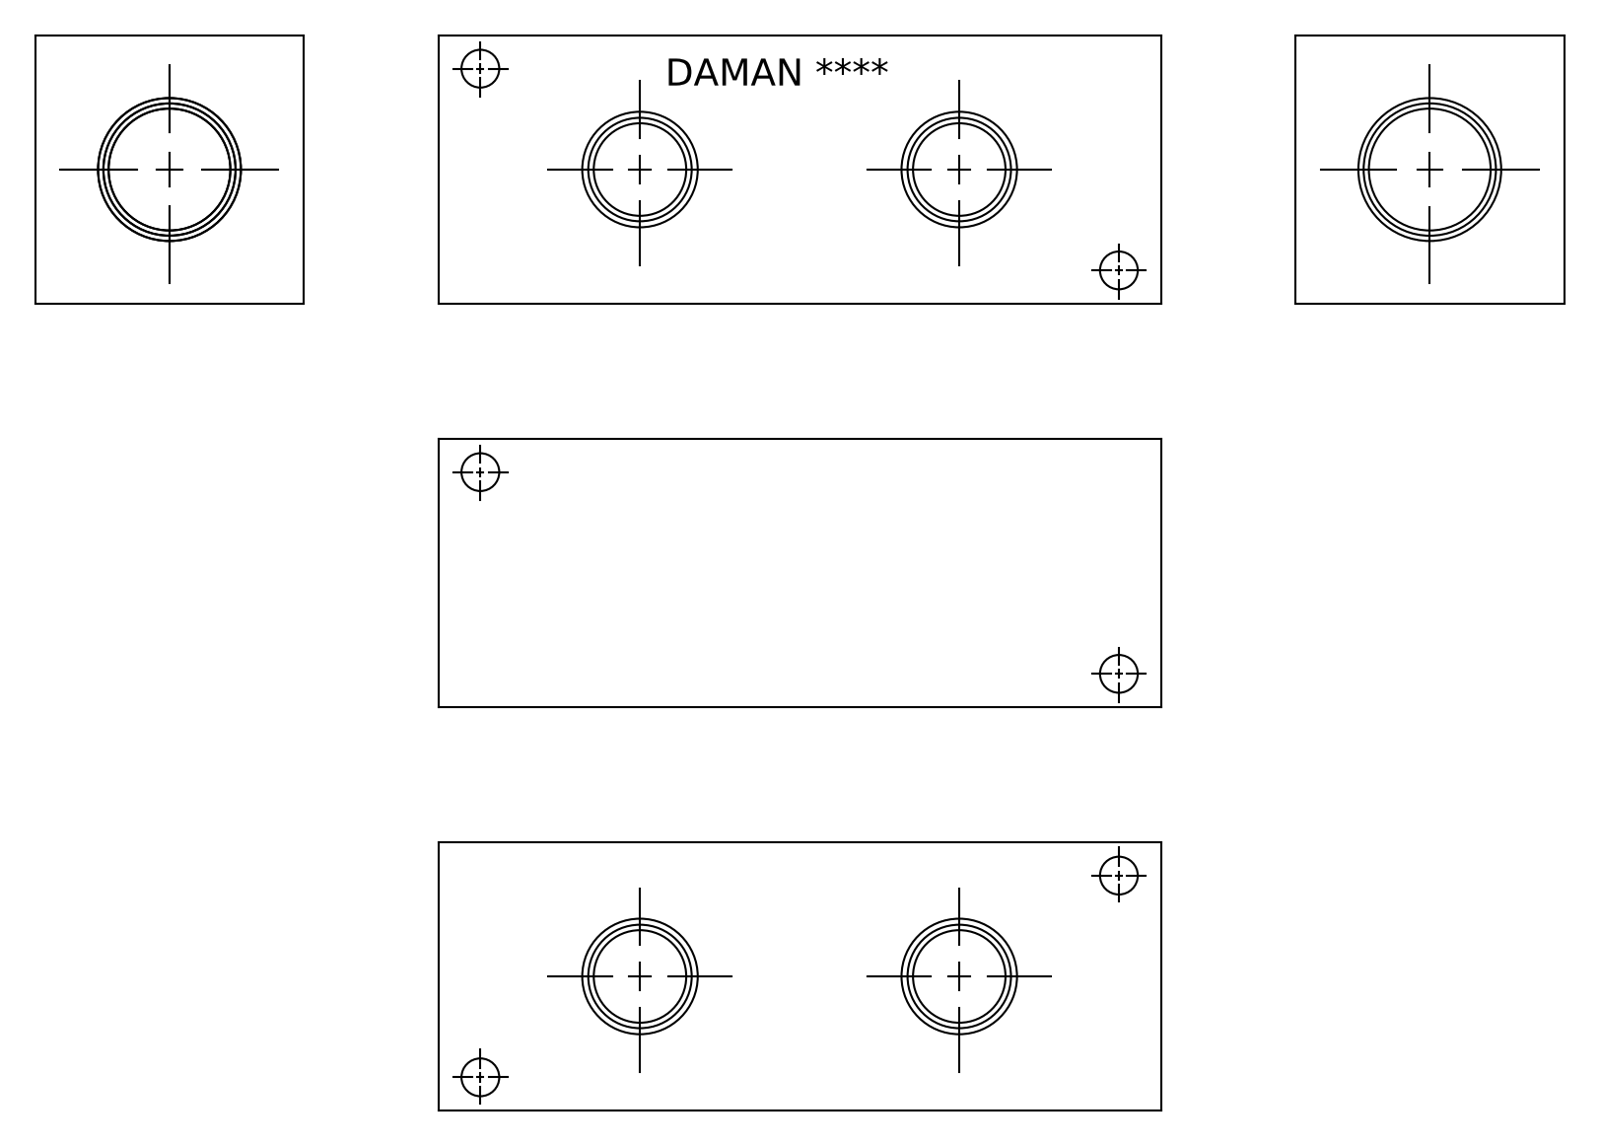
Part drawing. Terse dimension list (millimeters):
name: Part_+H1800208P_3D
written by: Autodesk Inventor 2020 (AUTOMOTIVE_DESIGN)
unit: mm
bodies: 1 solid, 351 faces (223 planar, 20 cylindrical, 108 other)
size: 136.53 × 50.8 × 50.8
volume: 299 630 mm³; area: 44 084 mm²
holes: 4× ⌀7.14, 2× ⌀17.48, 2× ⌀21.59, 1× ⌀23.01, 1× ⌀26.92
face distances: 50.8, 136.53, 15.37, 35.43, 15.85, 120.68, 20.06, 104.83, 50.76, 35.39
hole spacings: 126.52, 35.66, 35.69, 60.32, 92.45, 92.48
